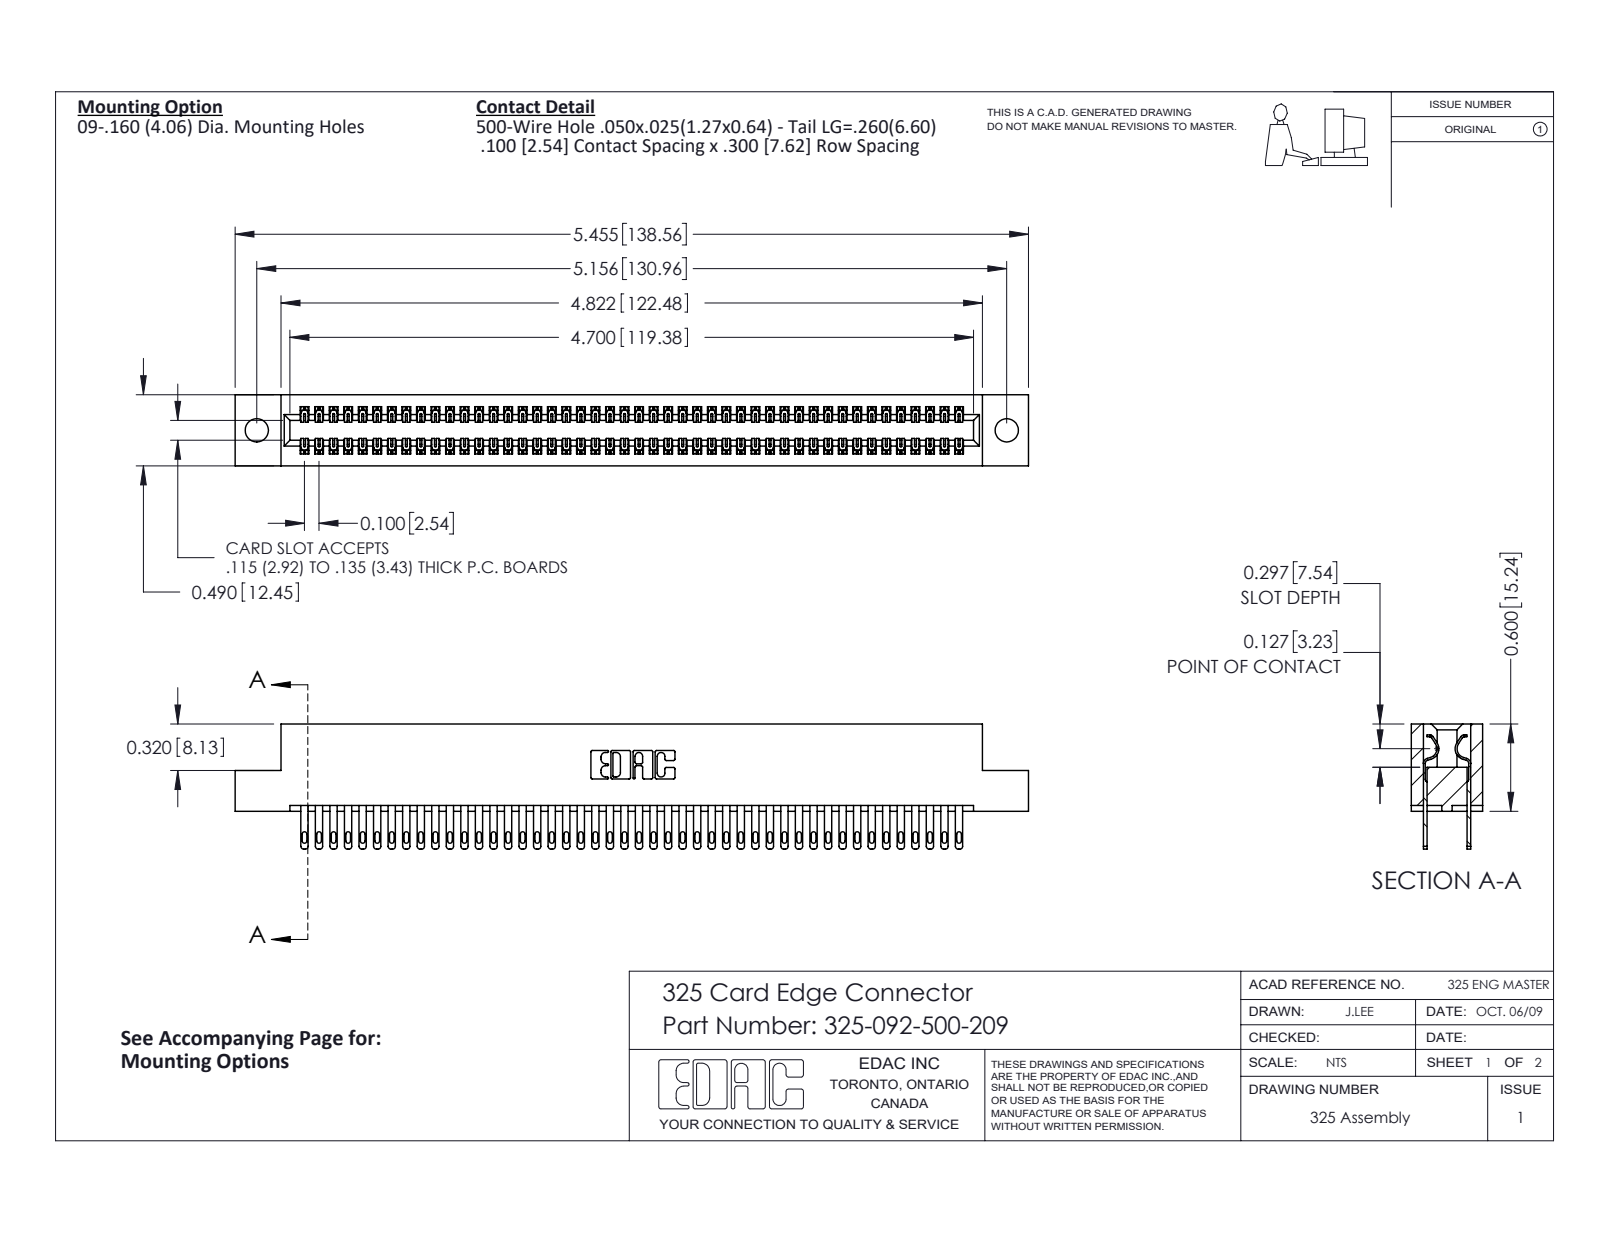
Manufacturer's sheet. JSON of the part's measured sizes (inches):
{"part_name": "325-092-500-209; 325 Part_.160 TH; 325-292-001_325-293-100", "step_written_by": "SolidWorks 2016 (CONFIG_CONTROL_DESIGN)", "units": "inches", "bodies": {"solids": 93, "faces": 4530, "planar": 2830, "cylindrical": 1700, "other": 0}, "overall_size": [5.455, 0.86, 0.49], "volume_in3": 1.097, "surface_area_in2": 35.23, "round_holes": [[0.16, 2]], "partial_cylinders_radius": [[0.006, 138], [0.016, 92], [0.02, 92], [0.01, 22], [0.007, 6], [0.031, 6], [0.026, 3], [0.014, 2]], "face_to_face_distances": [0.083, 0.407, 0.3, 0.107, 0.383, 0.025, 0.49, 0.325, 0.275, 0.56], "hole_center_spacings": [5.156]}
